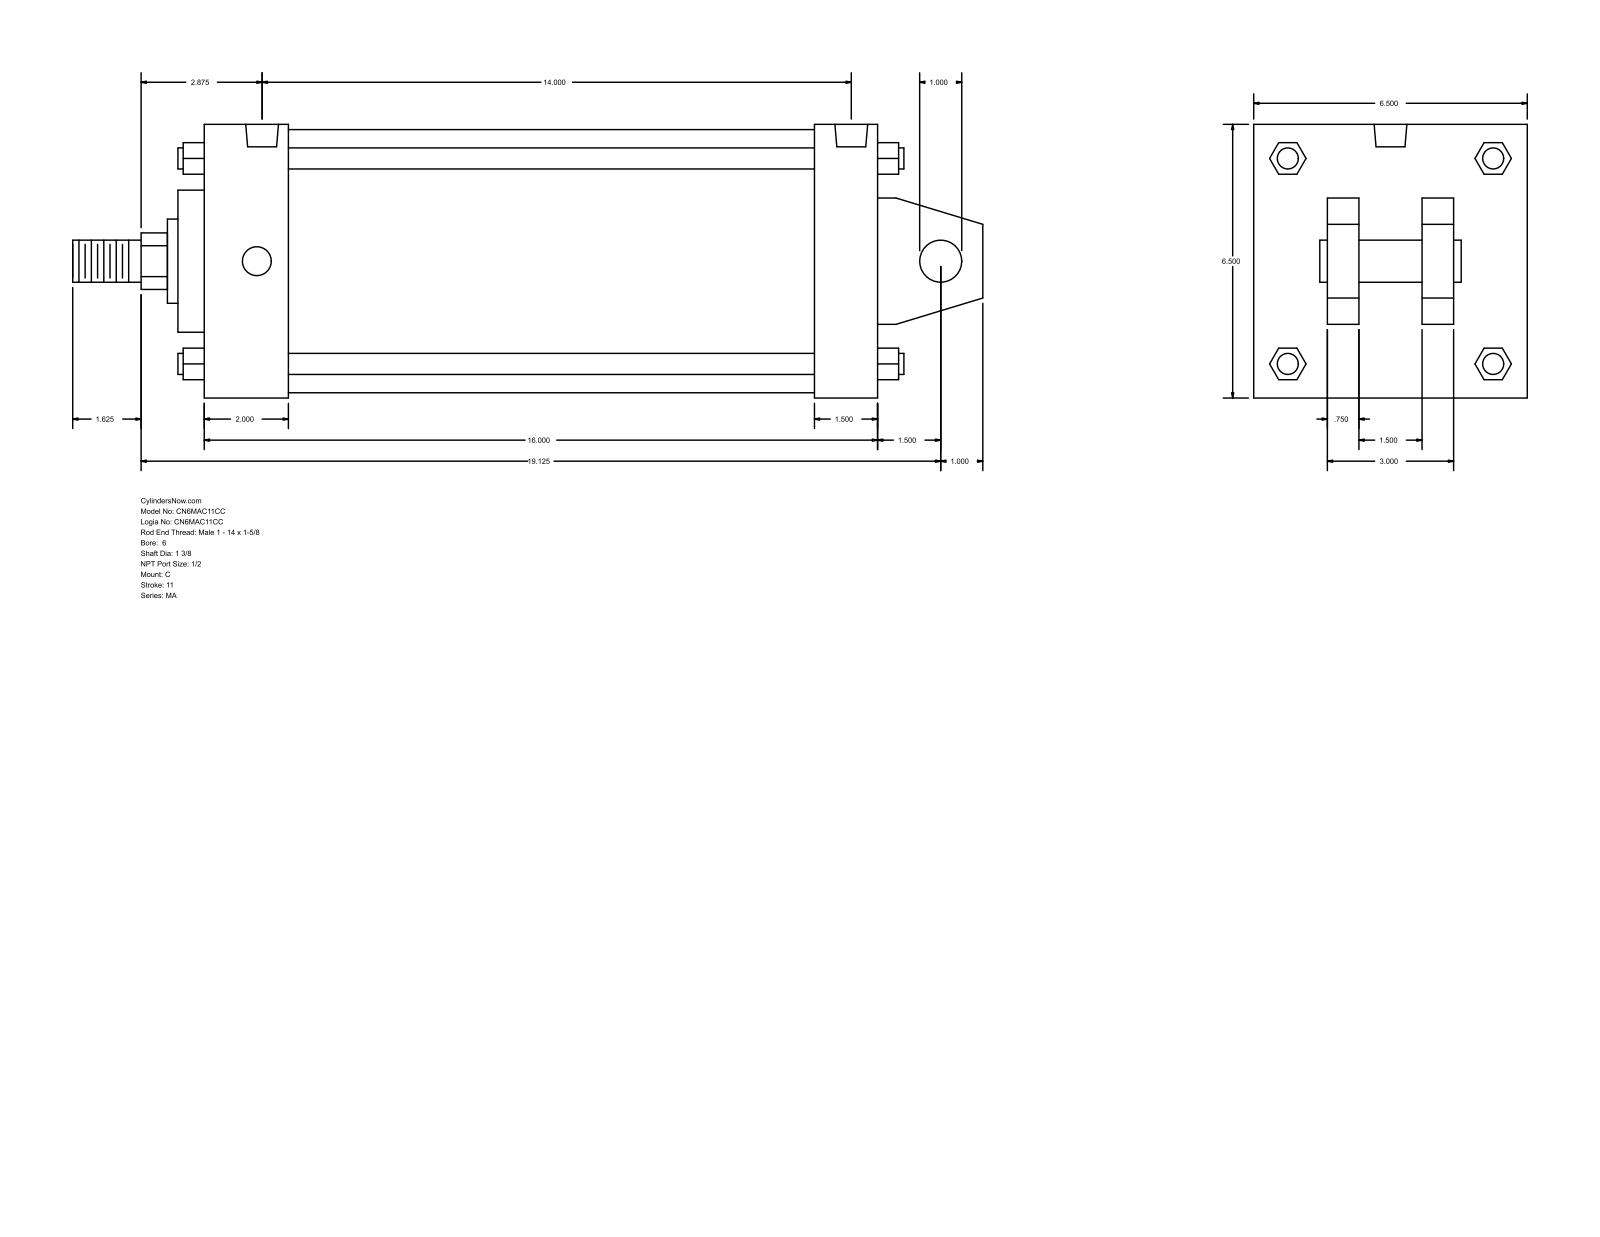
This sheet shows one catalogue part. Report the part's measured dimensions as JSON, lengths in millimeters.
{"part_name": "MA_C__0600_1.375", "step_written_by": "GSSL Pune (CONFIG_CONTROL_DESIGN)", "units": "millimeters", "bodies": {"solids": 0, "faces": 141, "planar": 109, "cylindrical": 32, "other": 0}, "overall_size": [549.27, 165.1, 165.1], "round_holes": [[17.46, 4], [19.77, 2]], "round_bosses_or_shafts": [[12.7, 4], [25.4, 2], [158.75, 1], [85.72, 1], [50.8, 1], [34.92, 1]], "partial_cylinders_radius": [[17.06, 1]], "face_to_face_distances": [165.1, 406.4, 38.1, 19.05, 63.5, 101.6, 50.8, 120.65, 44.45, 368.3], "hole_center_spacings": [355.6, 3.17, 3.18, 352.42, 355.59, 358.77]}
